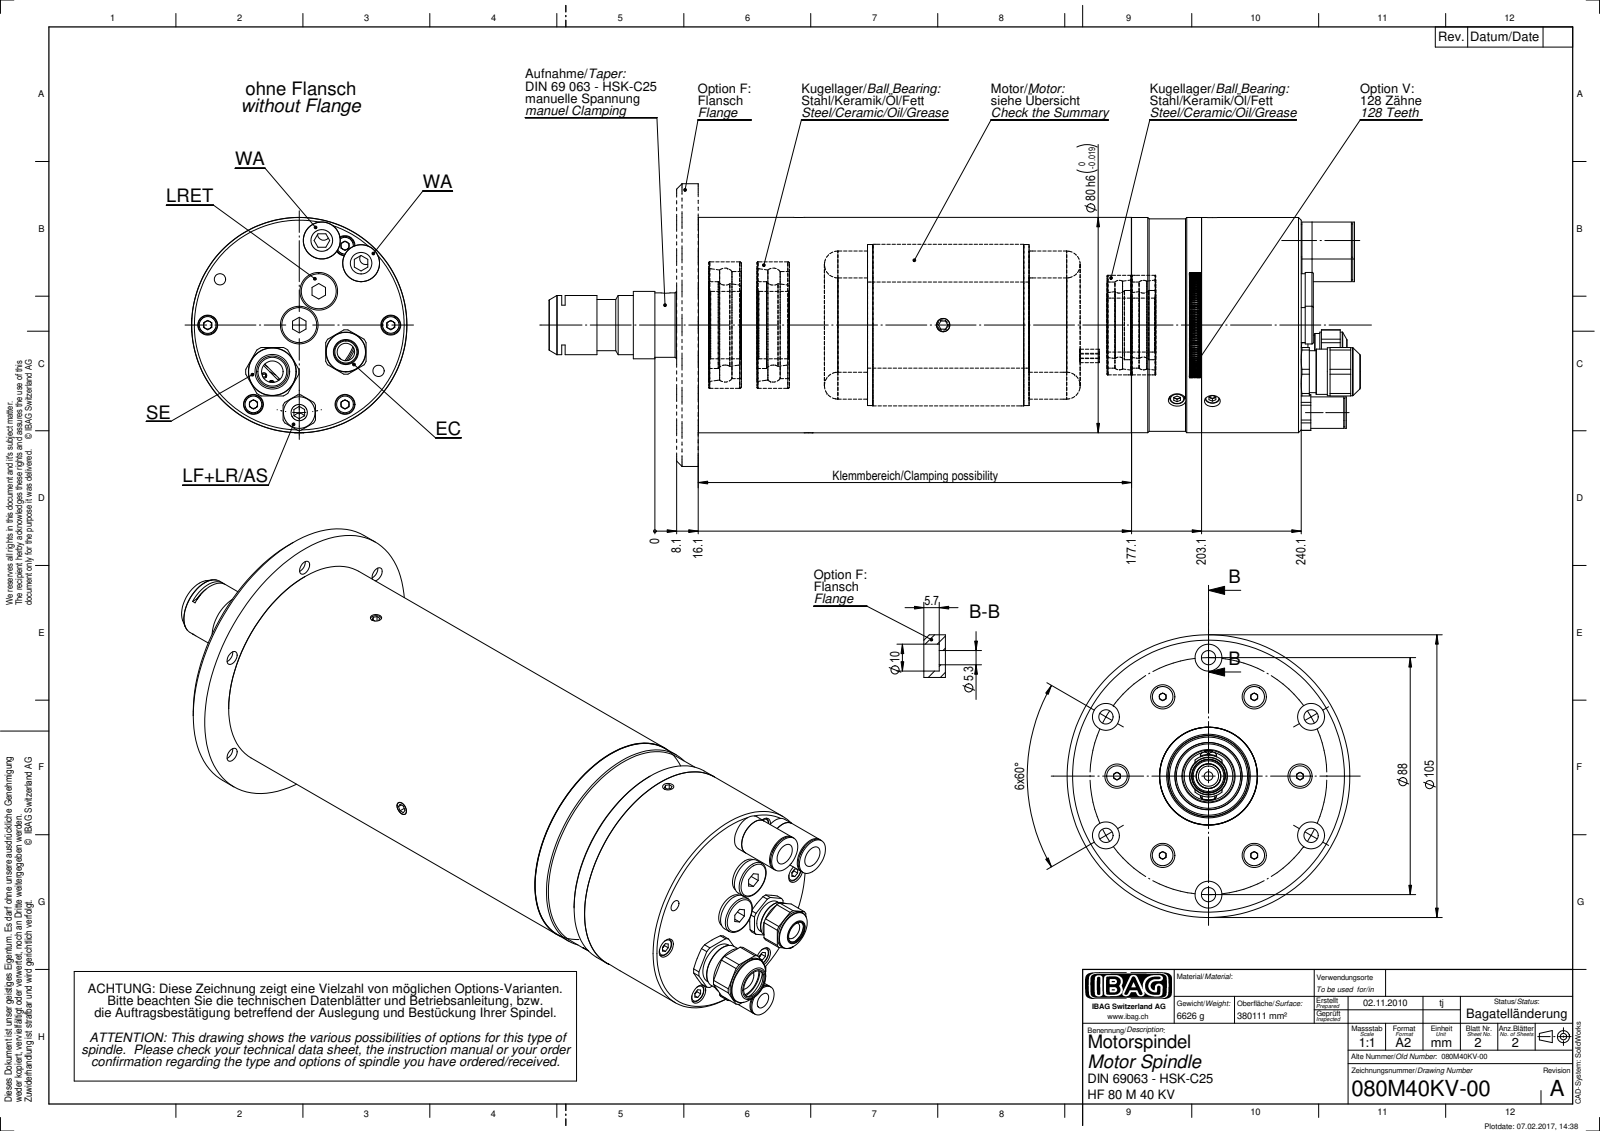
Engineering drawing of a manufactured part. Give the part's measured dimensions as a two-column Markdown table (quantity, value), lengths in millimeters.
| quantity | value |
| --- | --- |
| part name | 080M40KV-00A |
| STEP written by | SolidWorks 2014 (CONFIG_CONTROL_DESIGN) |
| units | millimeters |
| bodies | 0 solids, 483 faces (208 planar, 163 cylindrical, 112 other) |
| overall size | 310.4 × 80 × 80 |
| round holes (diameter × count) | 7.4 × 5, 4.2 × 3, 8 × 3, 3.3 × 2, 6.5 × 2, 2.9 × 1, 5.9 × 1, 6 × 1, 8.2 × 1, 10 × 1, 10.7 × 1, 16.2 × 1 |
| round bosses / shafts (diameter × count) | 7.64 × 6, 14 × 2, 13.7 × 2, 13.7 × 2, 13 × 2, 80 × 1, 79.9 × 1, 79.8 × 1 |
| partial cylindrical surfaces (radius × count) | 6.6 × 1, 8.25 × 1, 9.9 × 1 |
| main face-to-face distances | 232, 195, 37, 8, 187, 224, 169, 161, 26, 63 |
| hole center spacings | 34, 39.44, 48.08, 52.76, 32.5, 58.89, 65.68, 14 |
